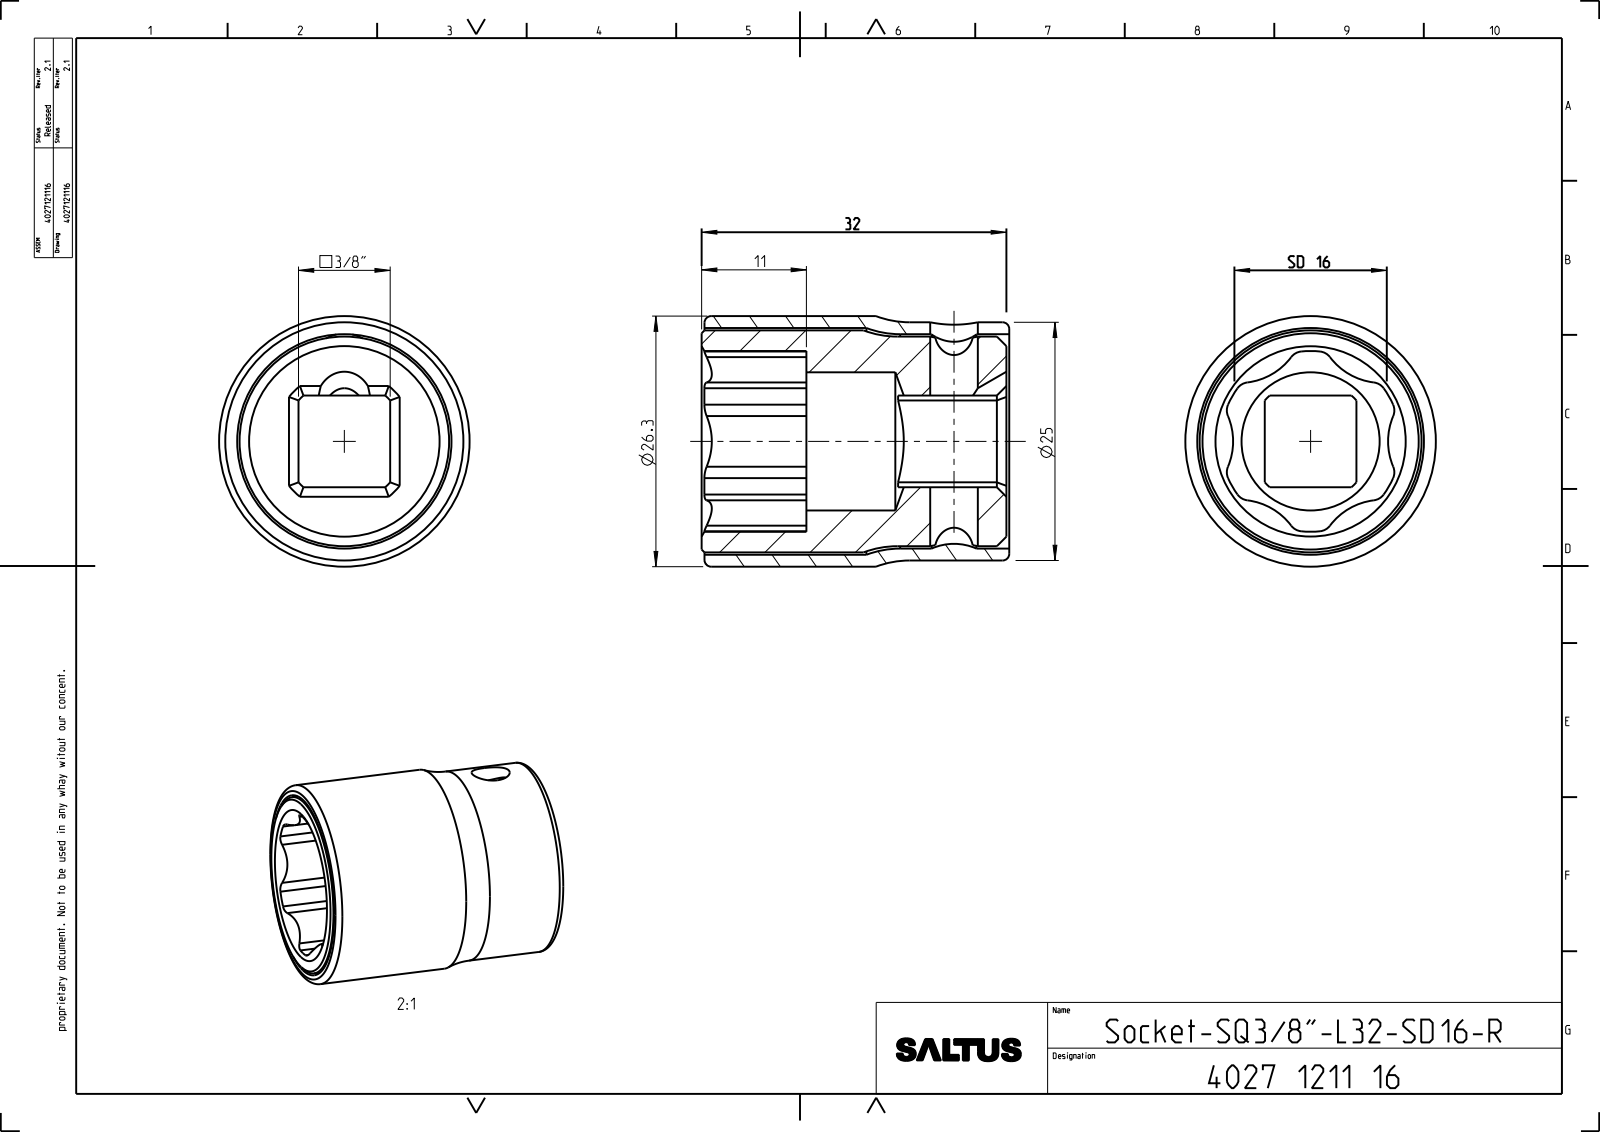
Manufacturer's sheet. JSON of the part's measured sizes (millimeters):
{"part_name": "4027120816; 4027042001; 4027121116_ASM", "step_written_by": "CREO PARAMETRIC BY PTC INC, 2022414 (CONFIG_CONTROL_DESIGN)", "units": "millimeters", "bodies": {"solids": 2, "faces": 92, "planar": 14, "cylindrical": 53, "other": 25}, "overall_size": [32.3, 26.3, 26.3], "volume_mm3": 10236, "surface_area_mm2": 9519, "round_holes": [[5, 1], [14.5, 1], [22.5, 1], [23.8, 1]], "round_bosses_or_shafts": [[26.3, 1], [25, 1], [23.3, 1], [22, 1]], "partial_cylinders_radius": [[1.5, 12], [6.8, 6], [3, 1], [6.45, 1], [9.48, 1]], "face_to_face_distances": [9.62, 32, 21, 11, 31.7, 10.7, 21.3, 32.3]}
